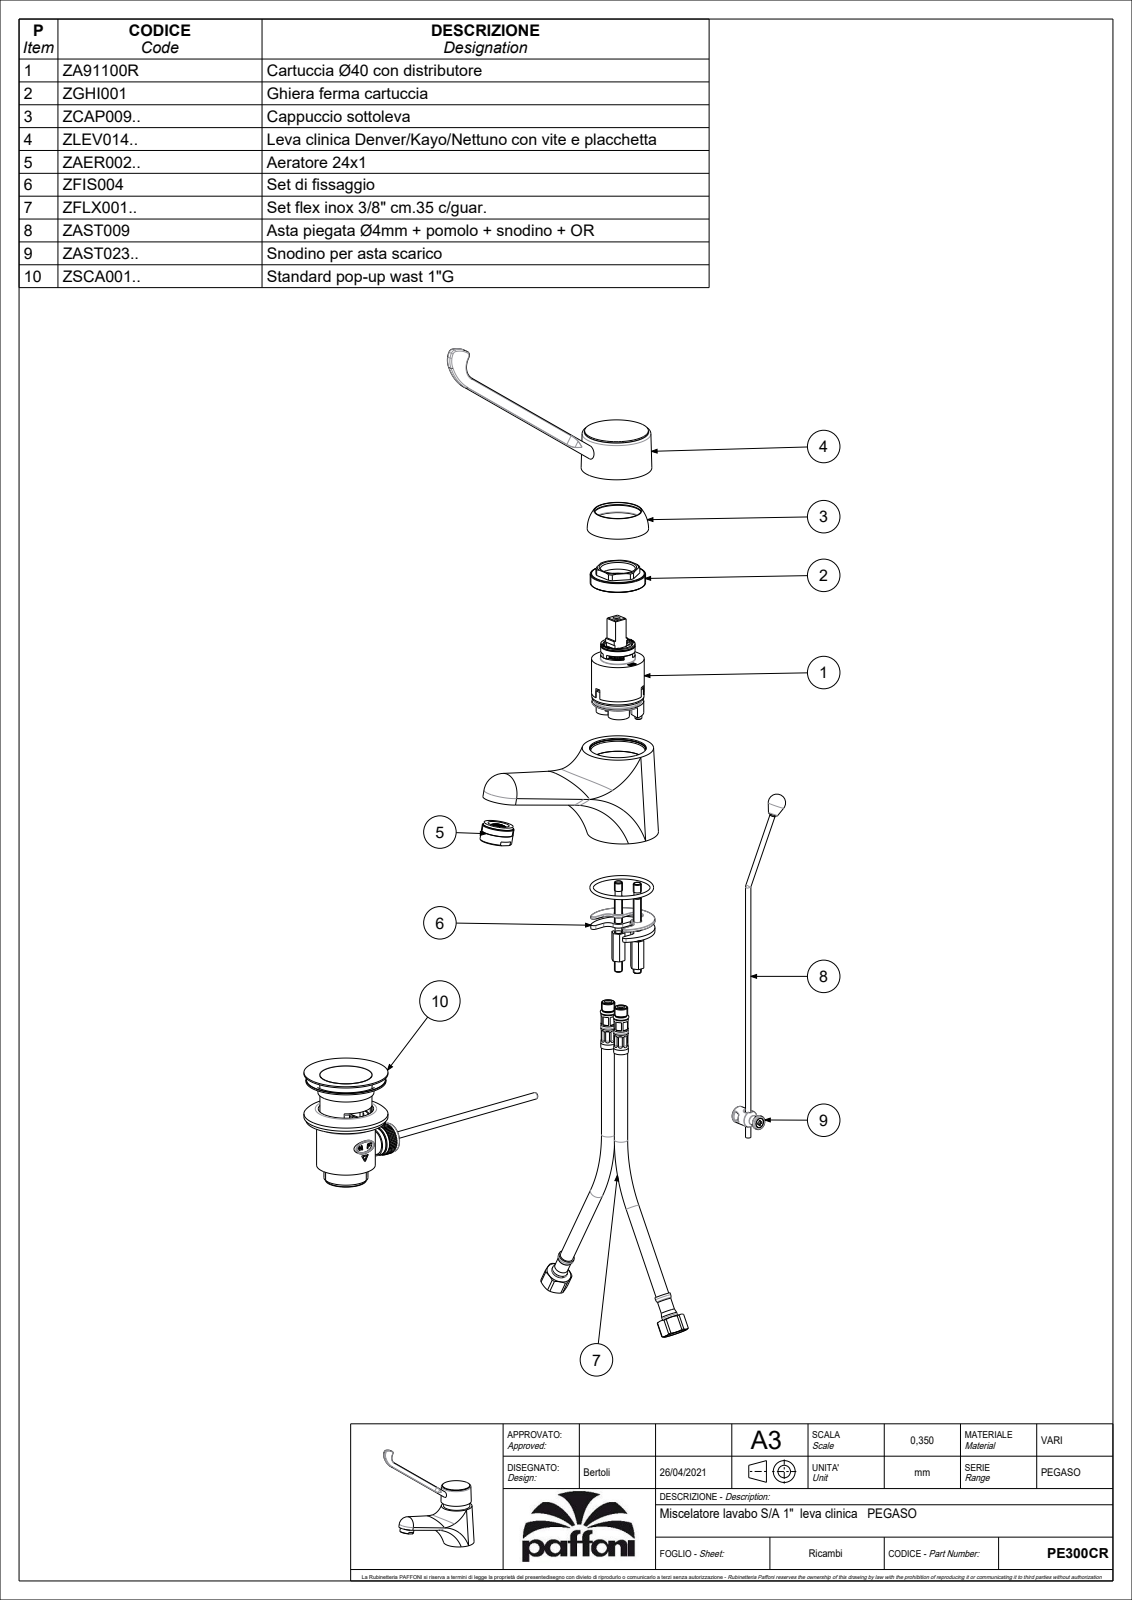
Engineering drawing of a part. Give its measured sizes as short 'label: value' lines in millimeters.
name: PE300CR_SW0001
written by: CREO PARAMETRIC BY PTC INC, 2022124 (CONFIG_CONTROL_DESIGN)
unit: mm
bodies: 4 solids, 2166 faces (1851 planar, 111 cylindrical, 204 other)
size: 211.88 × 208.58 × 53.5
volume: 177 696 mm³; area: 74 845 mm²
holes: 5× ⌀5.5, 2× ⌀7, 2× ⌀9, 2× ⌀11, 1× ⌀4, 1× ⌀5, 1× ⌀16, 1× ⌀17, 1× ⌀20, 1× ⌀21, 1× ⌀23, 1× ⌀24.5
bosses: 2× ⌀10, 1× ⌀47.85, 1× ⌀42, 1× ⌀33, 1× ⌀24, 1× ⌀20.9, 1× ⌀19.5, 1× ⌀18.8
rounds: 4× R0.3, 2× R1.5, 2× R2, 2× R6.5, 2× R7.5, 2× R18.3, 2× R25.63, 1× R2.5
face distances: 3.5, 6, 3, 4.5, 55.5, 4, 15.5, 77, 40, 22
hole spacings: 1.12, 3.16, 8.6, 9.6, 9.9, 10.97, 12.08, 12.65
